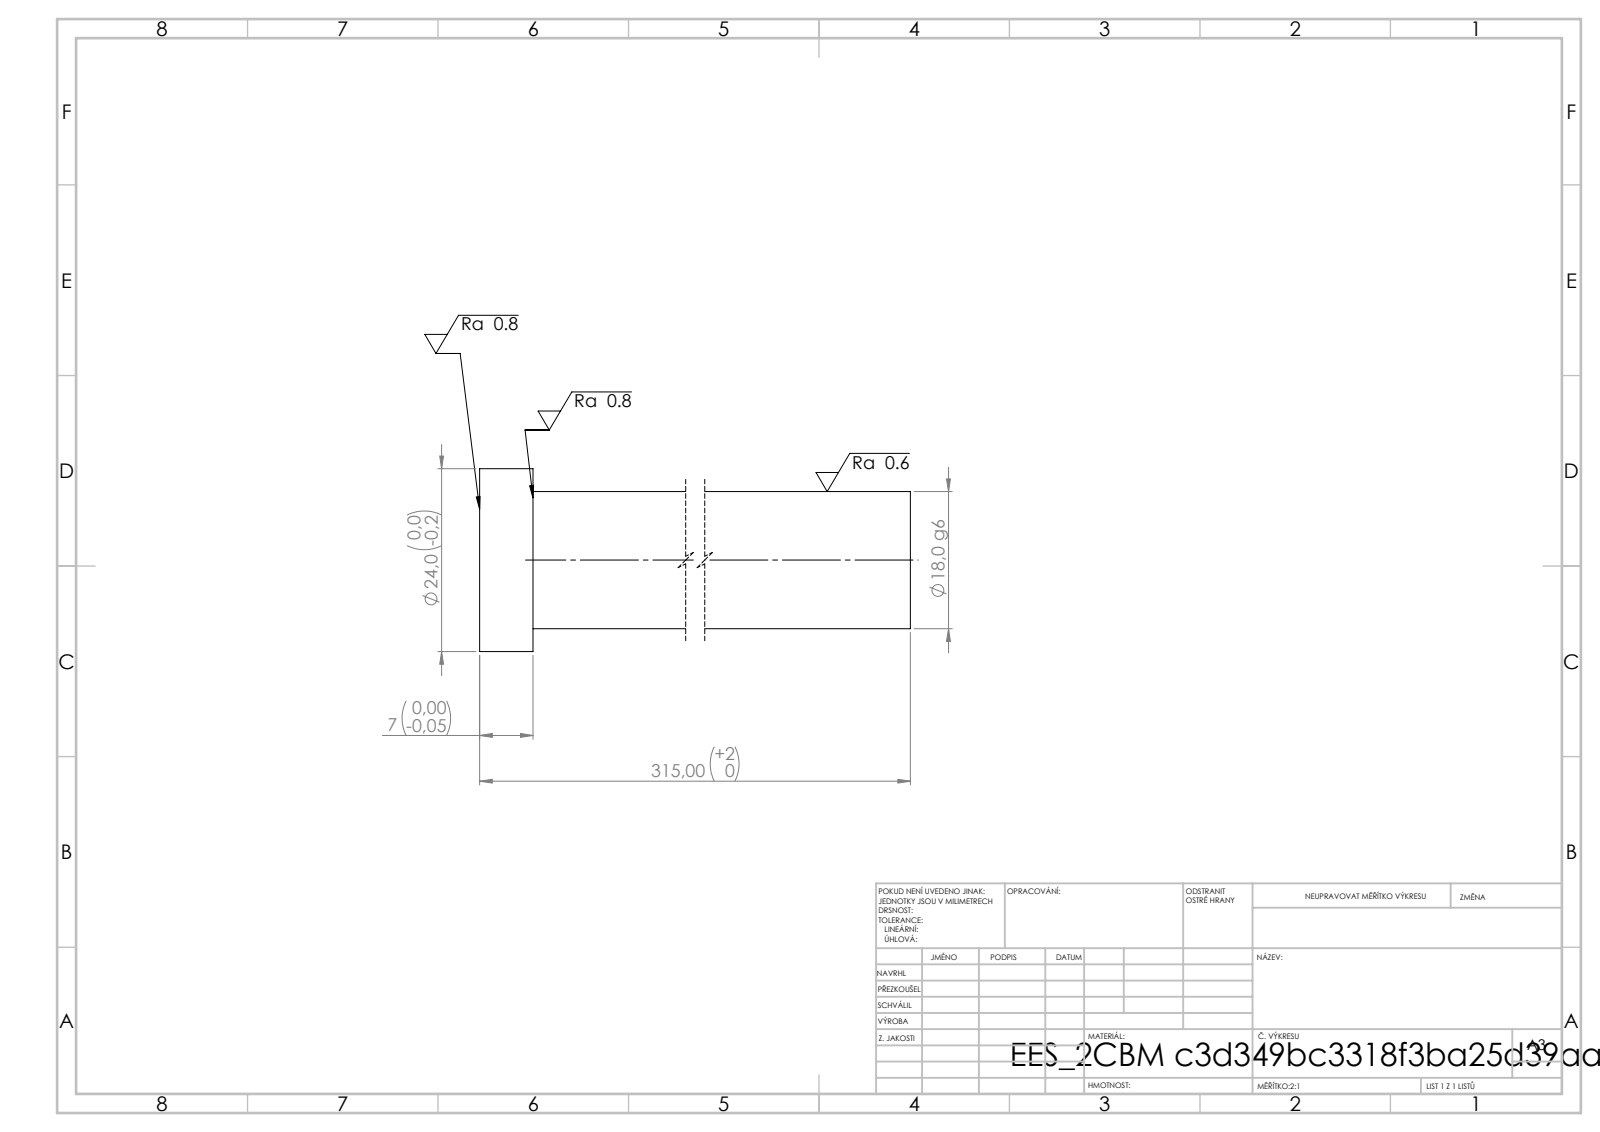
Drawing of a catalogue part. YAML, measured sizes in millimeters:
step_written_by: "SolidWorks 2019 (CONFIG_CONTROL_DESIGN)"
units: millimeters
bodies: {solids: 1, faces: 7, planar: 3, cylindrical: 4, other: 0}
overall_size: [315, 24, 24]
volume: 81543
surface_area: 18850
round_bosses_or_shafts:
  - {diameter: 24, count: 1}
  - {diameter: 18, count: 1}
face_to_face_distances: [315, 7, 308]
